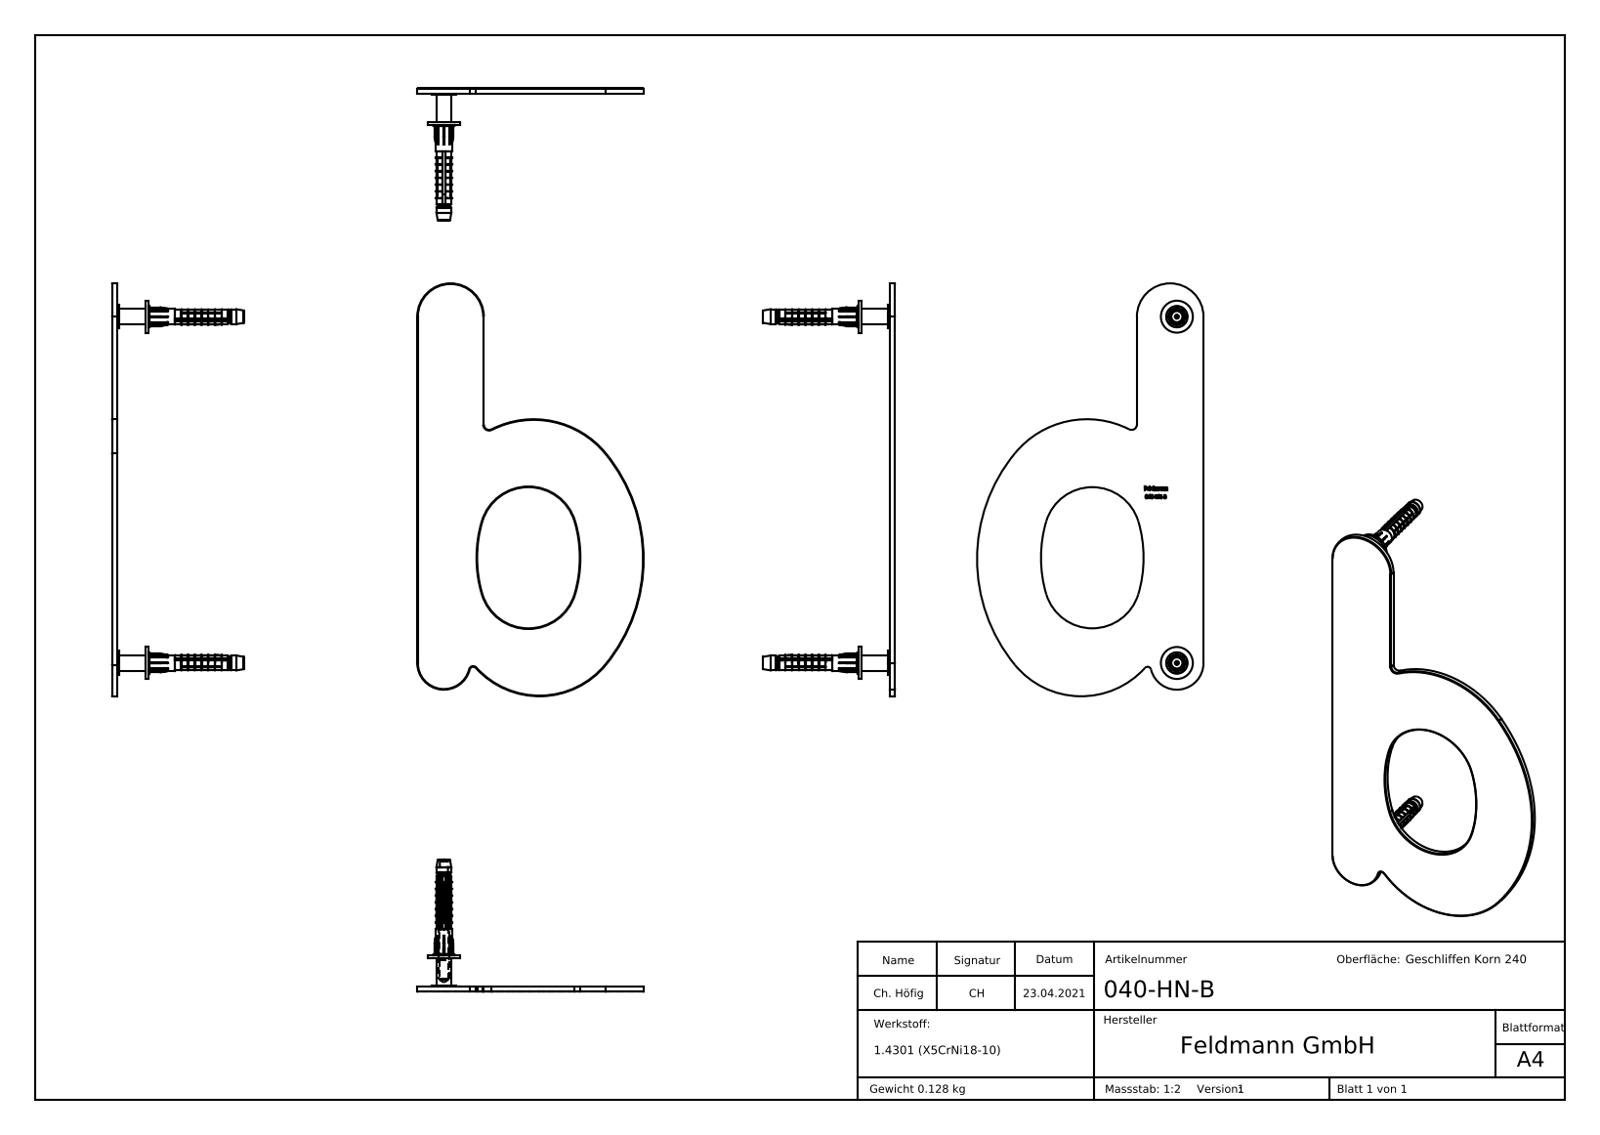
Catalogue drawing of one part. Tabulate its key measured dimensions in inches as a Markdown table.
| quantity | value |
| --- | --- |
| part name | 040-HN-X Teil4; 040-HN-X Teil2; 040-HN-X Teil3_040-HN-X Teil3; 040-HN-X Teil3 (+5 more) |
| STEP written by | SolidWorks 2018 (CONFIG_CONTROL_DESIGN) |
| units | inches |
| bodies | 7 solids, 1568 faces (364 planar, 389 cylindrical, 815 other) |
| overall size | 393.701 × 205.411 × 181.413 |
| volume | 1.049 in³ |
| surface area | 31.04 in² |
| round holes (diameter × count) | 0.13 × 2, 0.169 × 2 |
| round bosses / shafts (diameter × count) | 0.472 × 2, 0.354 × 2, 0.315 × 2, 0.236 × 2, 0.228 × 2, 0.22 × 2, 0.181 × 2, 0.157 × 2 |
| partial cylindrical surfaces (radius × count) | 0.004 × 22, 0.01 × 2, 0.138 × 2, 0.711 × 2, 0.052 × 1, 0.079 × 1, 0.394 × 1, 0.492 × 1 |
| main face-to-face distances | 0.079, 0.457, 0.535, 0.413, 0.043, 0.492, 0.039, 0.02, 0.098, 0.394 |
| hole center spacings | 5.118 |
